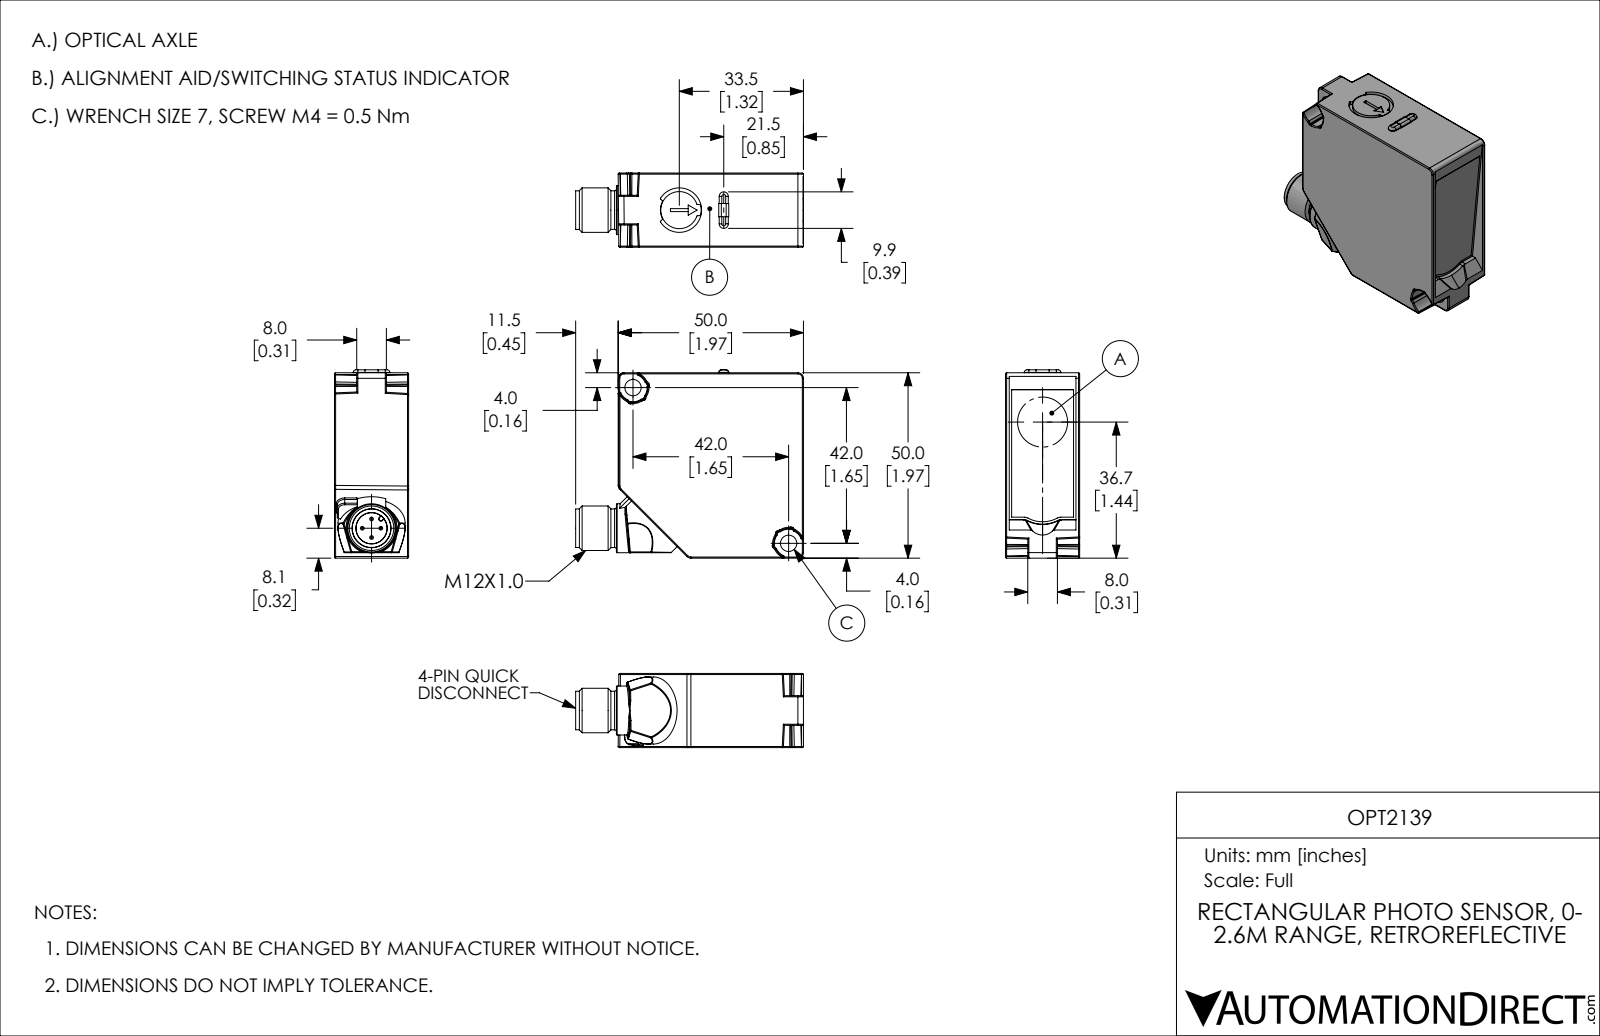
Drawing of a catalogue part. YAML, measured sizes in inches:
part_name: "OPT2139"
step_written_by: "SolidWorks 2019 (AUTOMOTIVE_DESIGN)"
units: inches
bodies: {solids: 2, faces: 342, planar: 110, cylindrical: 119, other: 113}
overall_size: [2.42, 2, 0.787]
volume: 2.816
surface_area: 16.5
round_holes:
  - {diameter: 0.173, count: 2}
  - {diameter: 0.472, count: 1}
  - {diameter: 0.713, count: 1}
round_bosses_or_shafts:
  - {diameter: 0.039, count: 4}
  - {diameter: 0.52, count: 1}
  - {diameter: 0.472, count: 1}
  - {diameter: 0.409, count: 1}
  - {diameter: 0.394, count: 1}
partial_cylinders:
  - {radius: 0.012, count: 63}
  - {radius: 0.008, count: 8}
  - {radius: 0.059, count: 5}
  - {radius: 0.079, count: 5}
  - {radius: 0.028, count: 4}
  - {radius: 0.048, count: 2}
  - {radius: 0.201, count: 1}
  - {radius: 0.232, count: 1}
face_to_face_distances: [0.787, 1.969, 0.039, 0.748, 0.236, 0.551, 0.197, 0.512, 0.058, 1.911]
hole_center_spacings: [2.339]
